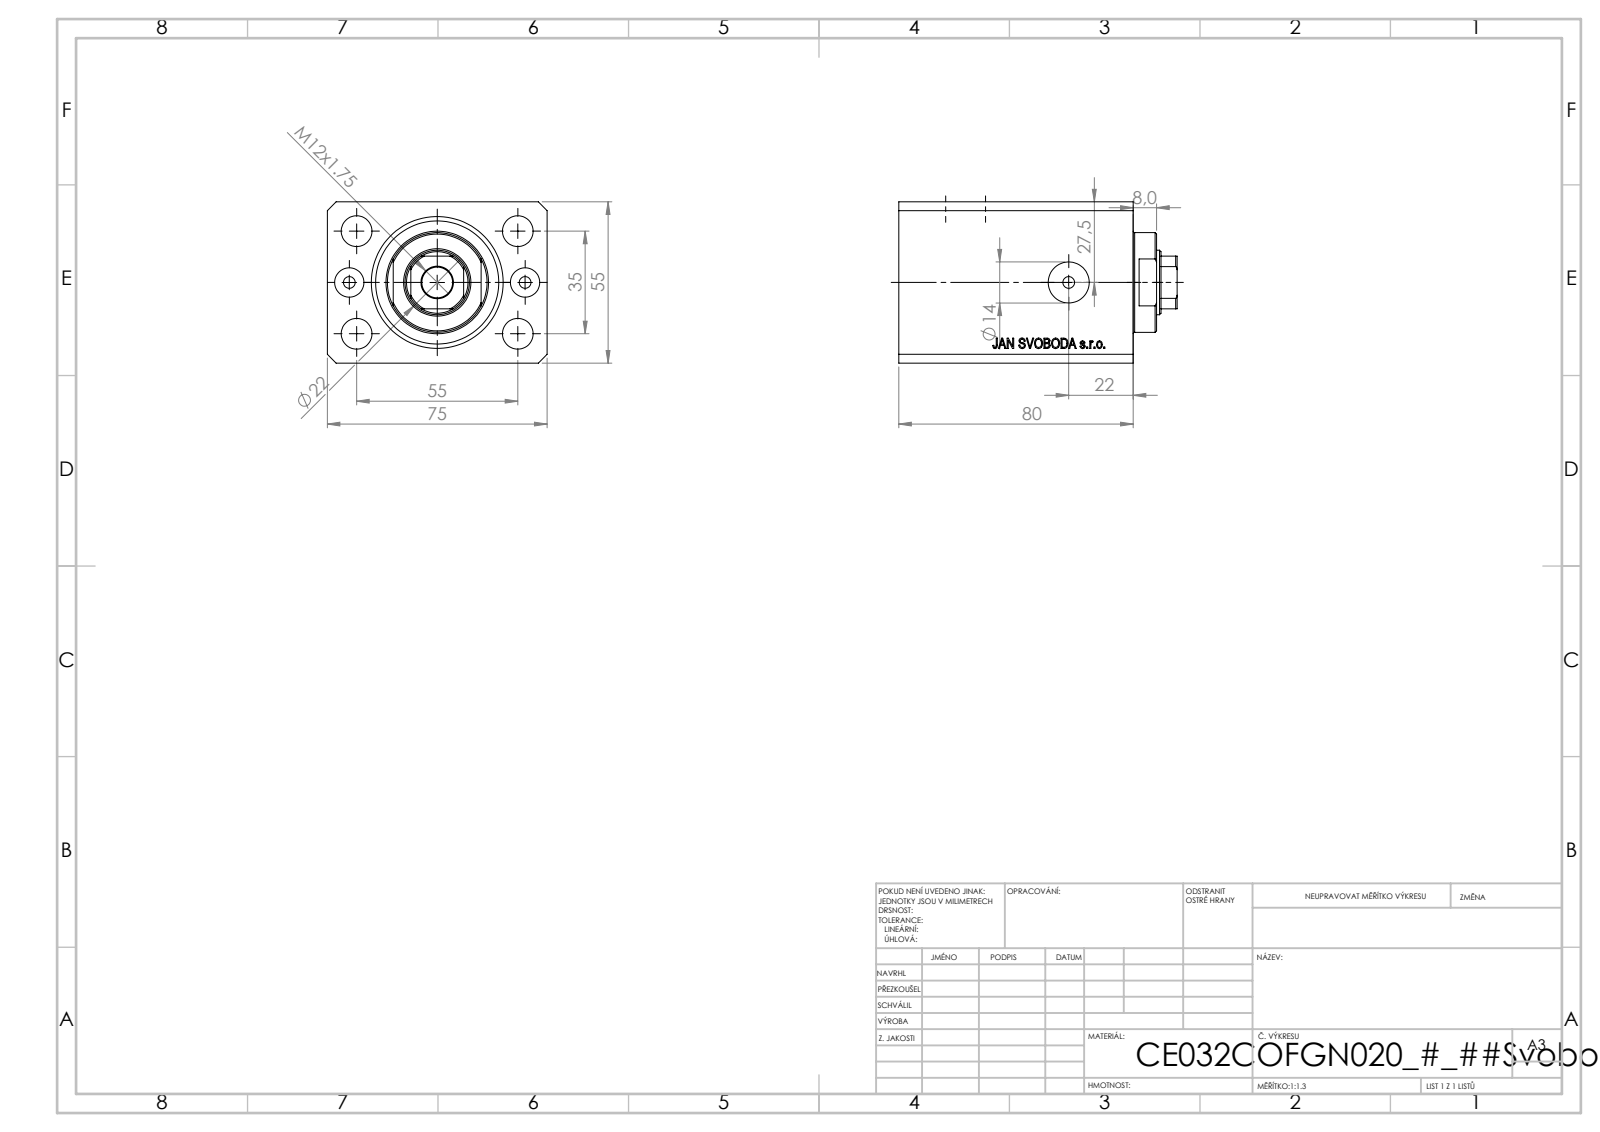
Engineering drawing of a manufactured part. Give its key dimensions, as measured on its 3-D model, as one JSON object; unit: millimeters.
{"part_name": "V250CE_C_Body; V250CE_VC_C; V250CE_C_VCP", "step_written_by": "SolidWorks 2019 (CONFIG_CONTROL_DESIGN)", "units": "millimeters", "bodies": {"solids": 3, "faces": 864, "planar": 428, "cylindrical": 44, "other": 392}, "overall_size": [95, 75, 55], "volume_mm3": 296611, "surface_area_mm2": 64227, "round_holes": [[10.5, 5], [4, 4], [10, 2], [14, 2], [22, 1], [32, 1], [45, 1]], "round_bosses_or_shafts": [[34, 1]], "partial_cylinders_radius": [[10.5, 1]], "face_to_face_distances": [55, 75, 80, 15, 65, 9.9, 55.1, 70.1, 87.66, 78.1], "hole_center_spacings": [17.68, 32.6, 60.1, 30, 35, 55, 65.19, 36]}
